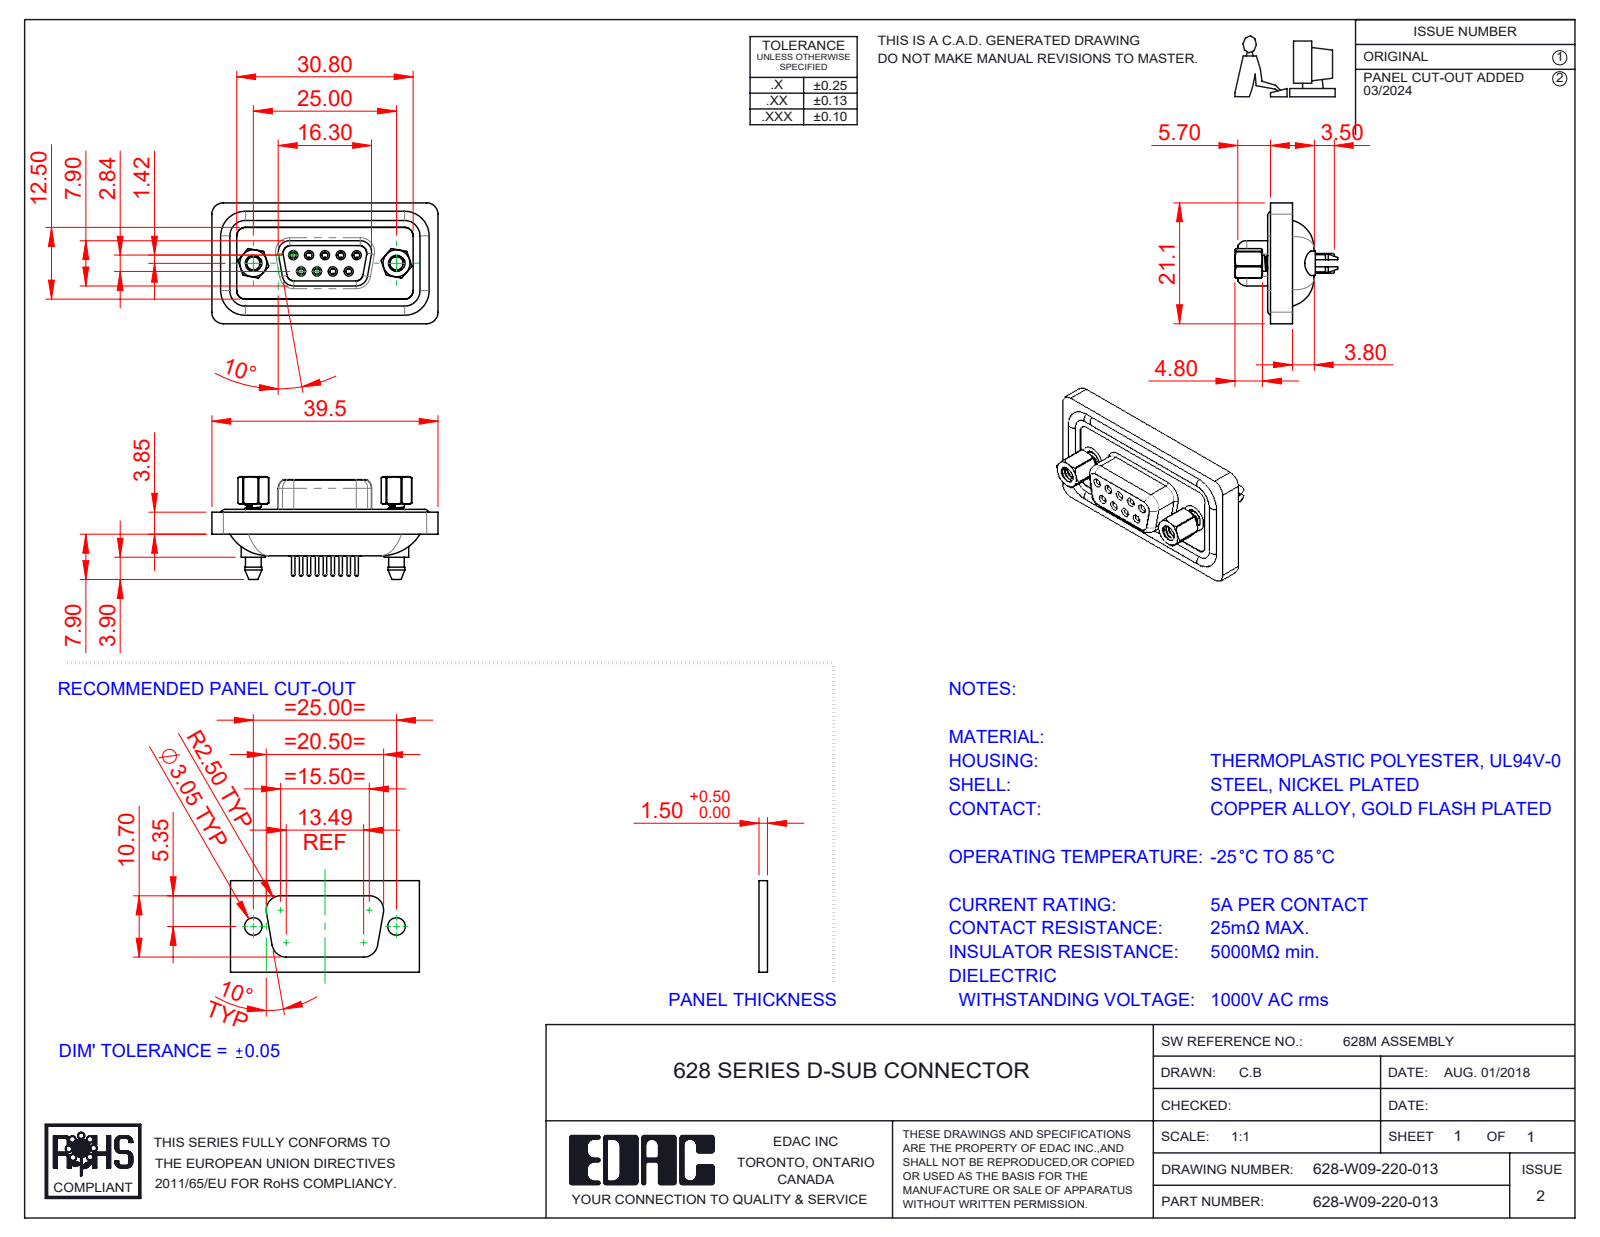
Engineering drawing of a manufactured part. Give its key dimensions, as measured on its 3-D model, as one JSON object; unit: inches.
{"part_name": "628W Contact Row 1_20; 628W Contact Row 2_20; 628W 4-40 Hex Standoff; 628-W09-220-013 (+4 more)", "step_written_by": "SolidWorks 2020 (CONFIG_CONTROL_DESIGN)", "units": "inches", "bodies": {"solids": 17, "faces": 984, "planar": 250, "cylindrical": 441, "other": 293}, "overall_size": [1.555, 0.831, 0.687], "volume_in3": 0.311, "surface_area_in2": 12.03, "round_holes": [[0.039, 9], [0.043, 9], [0.059, 9], [0.067, 9], [0.071, 9], [0.079, 9], [0.089, 2], [0.09, 2], [0.157, 2], [0.167, 2], [0.189, 2]], "round_bosses_or_shafts": [[0.063, 13], [0.087, 9], [0.024, 9], [0.213, 2], [0.193, 2], [0.11, 2]], "partial_cylinders_radius": [[0.059, 16], [0.079, 16], [0.053, 8], [0.063, 6], [0.02, 4], [0.035, 4], [0.069, 4], [0.106, 4]], "face_to_face_distances": [0.016, 0.043, 0.108, 0.02, 0.148, 0.039, 0.152, 0.132, 0.295, 0.063], "hole_center_spacings": [0.124, 0.109, 0.218, 0.198, 0.198, 0.327, 0.28, 0.294]}
